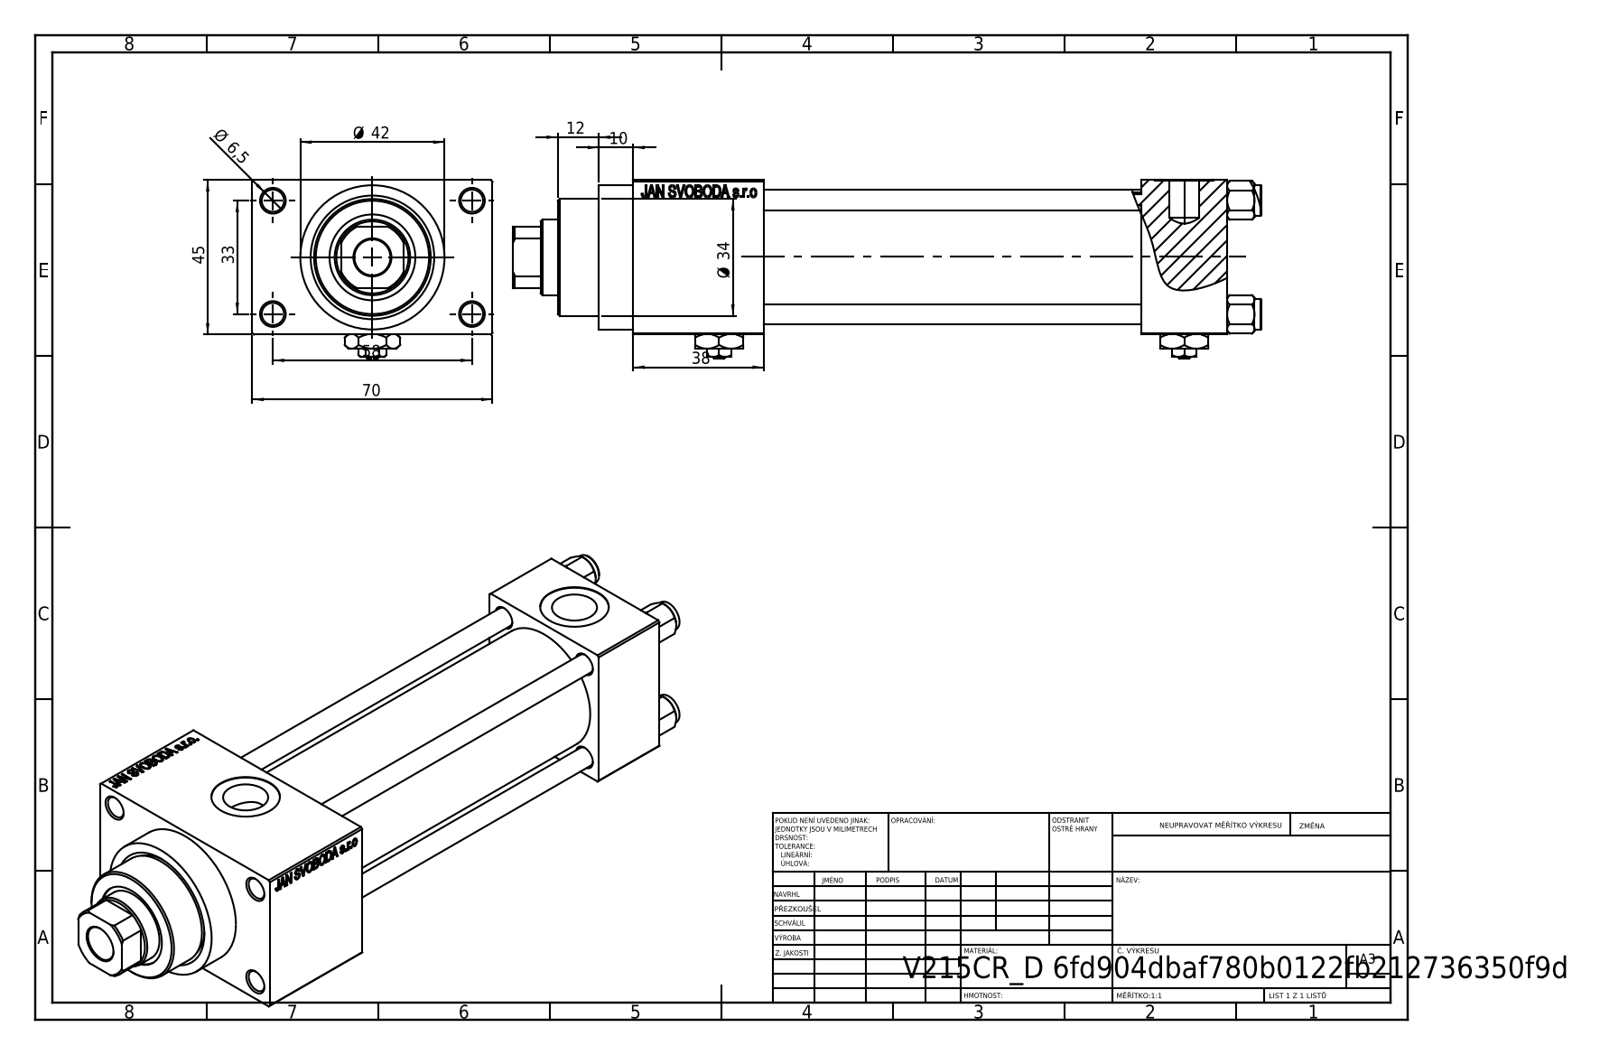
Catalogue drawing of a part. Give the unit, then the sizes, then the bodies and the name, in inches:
Units: inches
Overall size (bounding box): 8.583 × 2.756 × 2.047
Round holes (diameter × count): ⌀0.236 ×4, ⌀0.256 ×4, ⌀0.276 ×2, ⌀0.518 ×2, ⌀0.787 ×2, ⌀0.413 ×1, ⌀0.866 ×1, ⌀0.945 ×1, ⌀0.984 ×1, ⌀1.26 ×1, ⌀1.299 ×1
Round bosses / shafts (diameter × count): ⌀0.354 ×4, ⌀1.654 ×1, ⌀1.496 ×1, ⌀1.339 ×1
Partial cylindrical surfaces — rounded edges, fillets, slot ends (radius × count): R0.413 ×1
Main face-to-face distances: 1.772, 0.984, 0.492, 2.264, 4.331, 5.315, 5.827, 1.496, 2.756, 6.811
Hole centre spacings: 0.488, 0.924, 1.307, 1.314, 1.392, 1.795, 2.219, 1.299
Volume: 17.86 in³ · Surface area: 159.6 in²
Bodies: 13 solids, 1204 faces (542 planar, 100 cylindrical, 562 other)
Part name (STEP PRODUCT): V215CR_D_TYCINKA; Zatka_pro_OIL_PORT; V215_VC_A; NUT_M5_D (+2 more)
STEP written by: SolidWorks 2019 (CONFIG_CONTROL_DESIGN)
